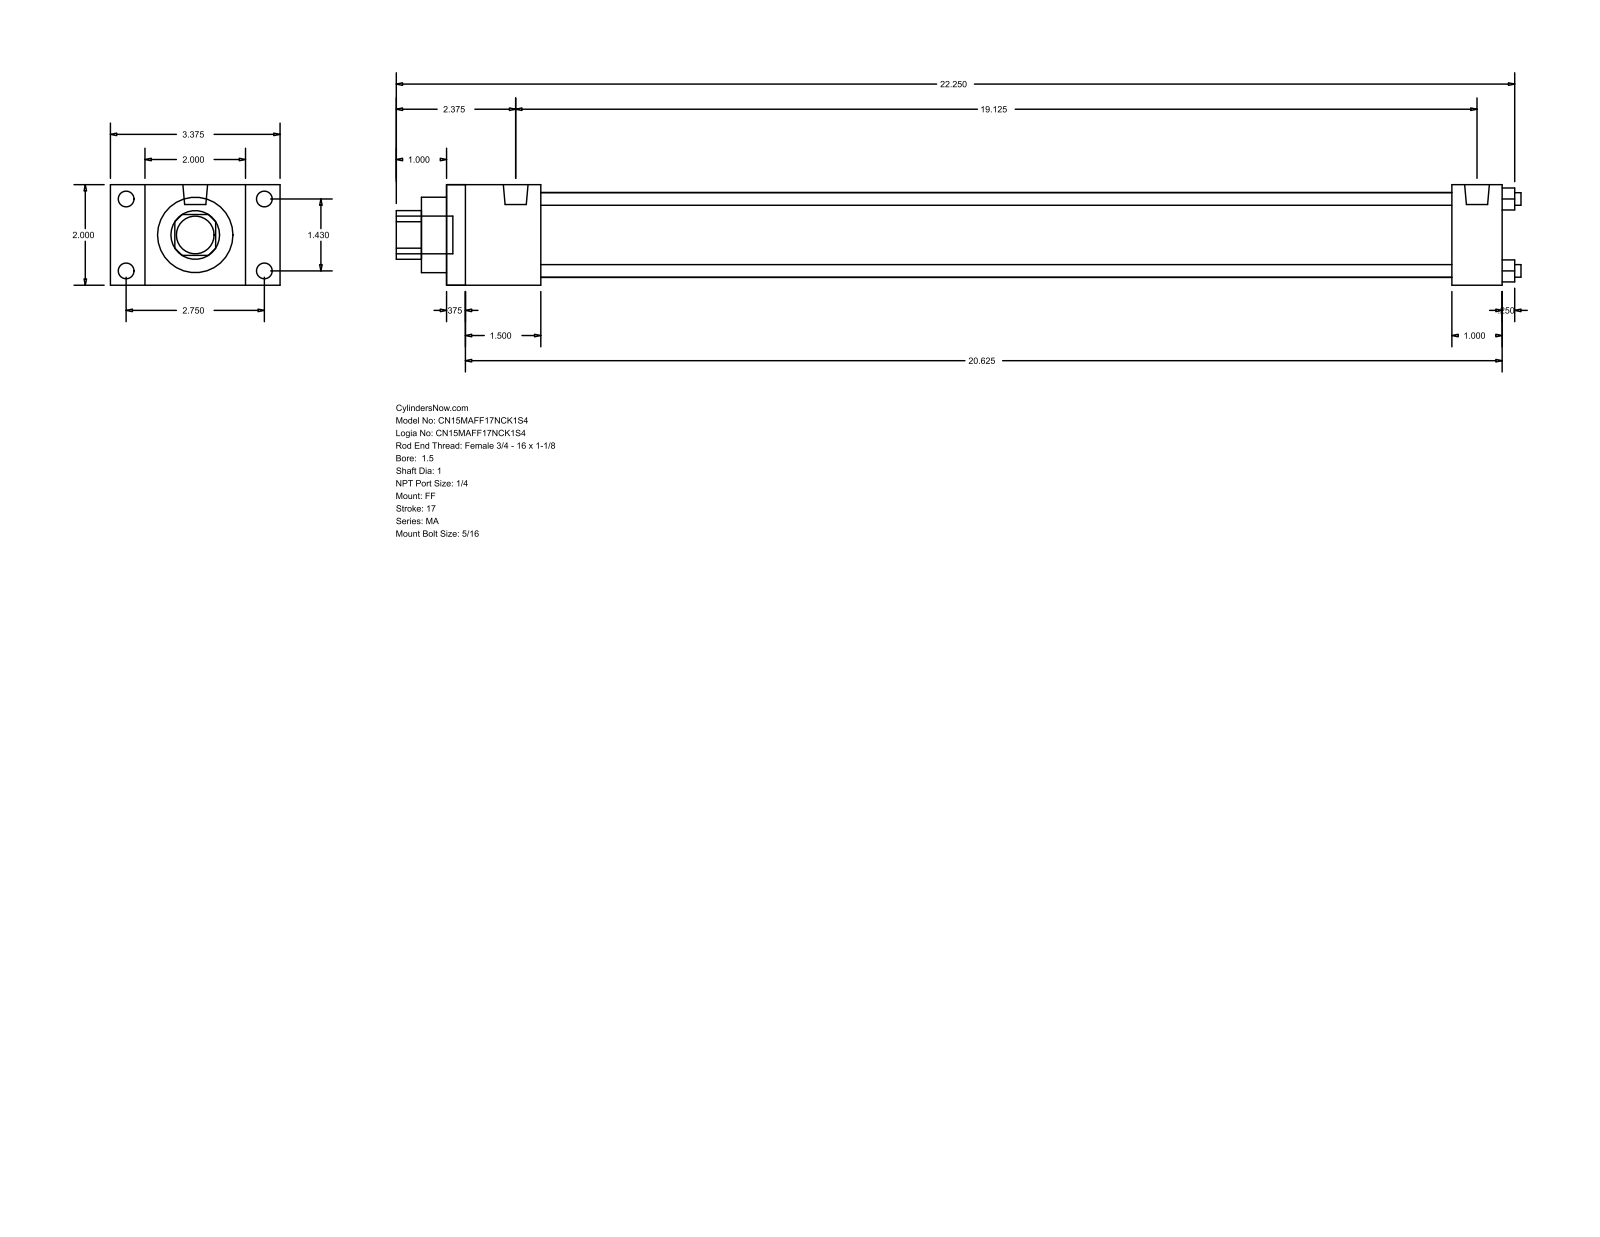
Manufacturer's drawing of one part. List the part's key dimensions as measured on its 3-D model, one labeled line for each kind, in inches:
Part name (STEP PRODUCT): MA_FF__0150_1
STEP written by: GSSL Pune (CONFIG_CONTROL_DESIGN)
Units: inches
Bodies: 0 solids, 92 faces (64 planar, 28 cylindrical, 0 other)
Overall size (bounding box): 22.375 × 3.375 × 2
Round holes (diameter × count): ⌀0.25 ×4, ⌀1 ×1, ⌀1.5 ×1, ⌀1.69 ×1
Round bosses / shafts (diameter × count): ⌀0.313 ×8, ⌀0.492 ×2, ⌀0.75 ×1
Partial cylindrical surfaces — rounded edges, fillets, slot ends (radius × count): R0.484 ×1
Main face-to-face distances: 2, 21, 0.375, 20.625, 1, 1.875, 20, 1.5, 19.625, 18.125
Hole centre spacings: 1.011, 1.43, 2.022
